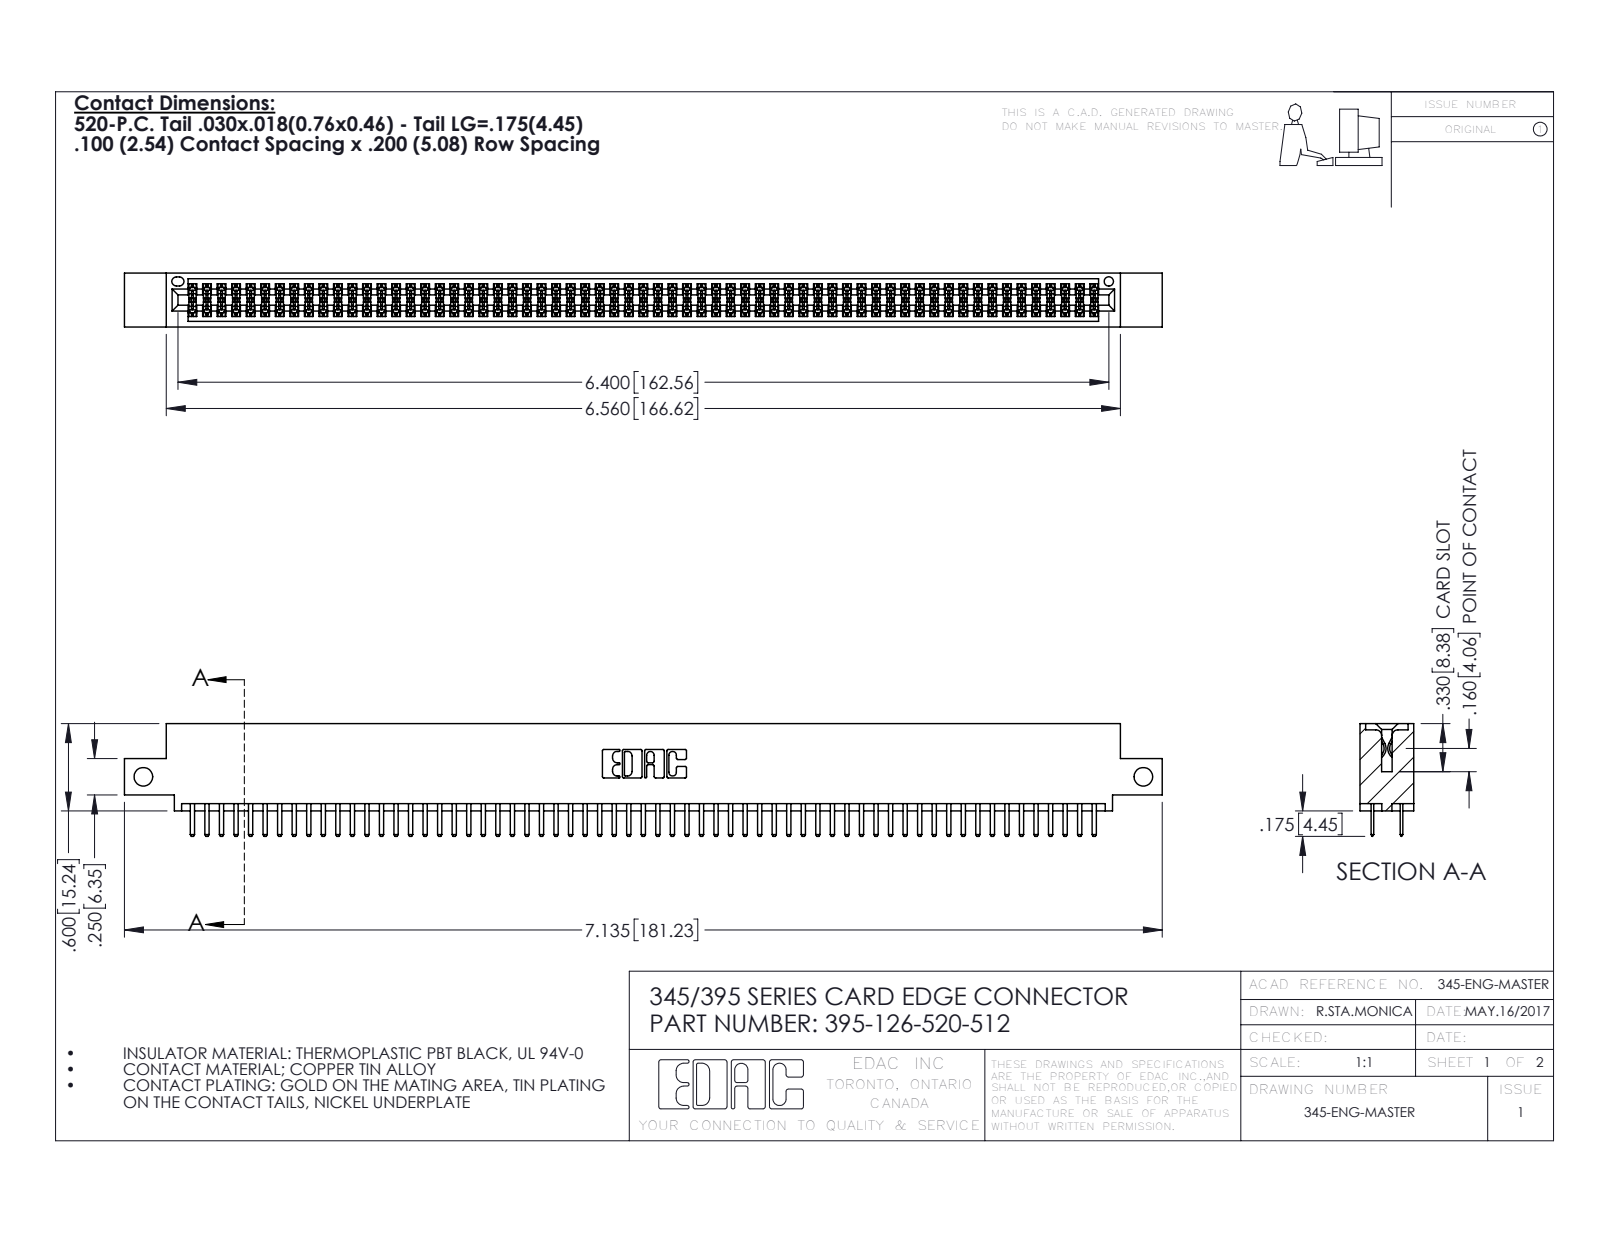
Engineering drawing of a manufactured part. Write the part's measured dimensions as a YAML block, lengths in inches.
part_name: "395-126-520-512; 345-292-001_345-293-120; 345 Part_0.110 Offset - Side Mount"
step_written_by: "SolidWorks 2016 (CONFIG_CONTROL_DESIGN)"
units: inches
bodies: {solids: 127, faces: 6934, planar: 4494, cylindrical: 2440, other: 0}
overall_size: [7.135, 0.775, 0.37]
volume: 1.073
surface_area: 40.67
round_holes:
  - {diameter: 0.128, count: 2}
  - {diameter: 0.064, count: 1}
partial_cylinders:
  - {radius: 0.006, count: 189}
  - {radius: 0.01, count: 130}
  - {radius: 0.01, count: 22}
  - {radius: 0.007, count: 6}
  - {radius: 0.031, count: 6}
  - {radius: 0.026, count: 3}
  - {radius: 0.014, count: 2}
  - {radius: 0.019, count: 2}
face_to_face_distances: [0.072, 0.298, 0.2, 0.37, 0.098, 0.272, 0.025, 0.225, 0.022, 0.072]
hole_center_spacings: [6.875]
